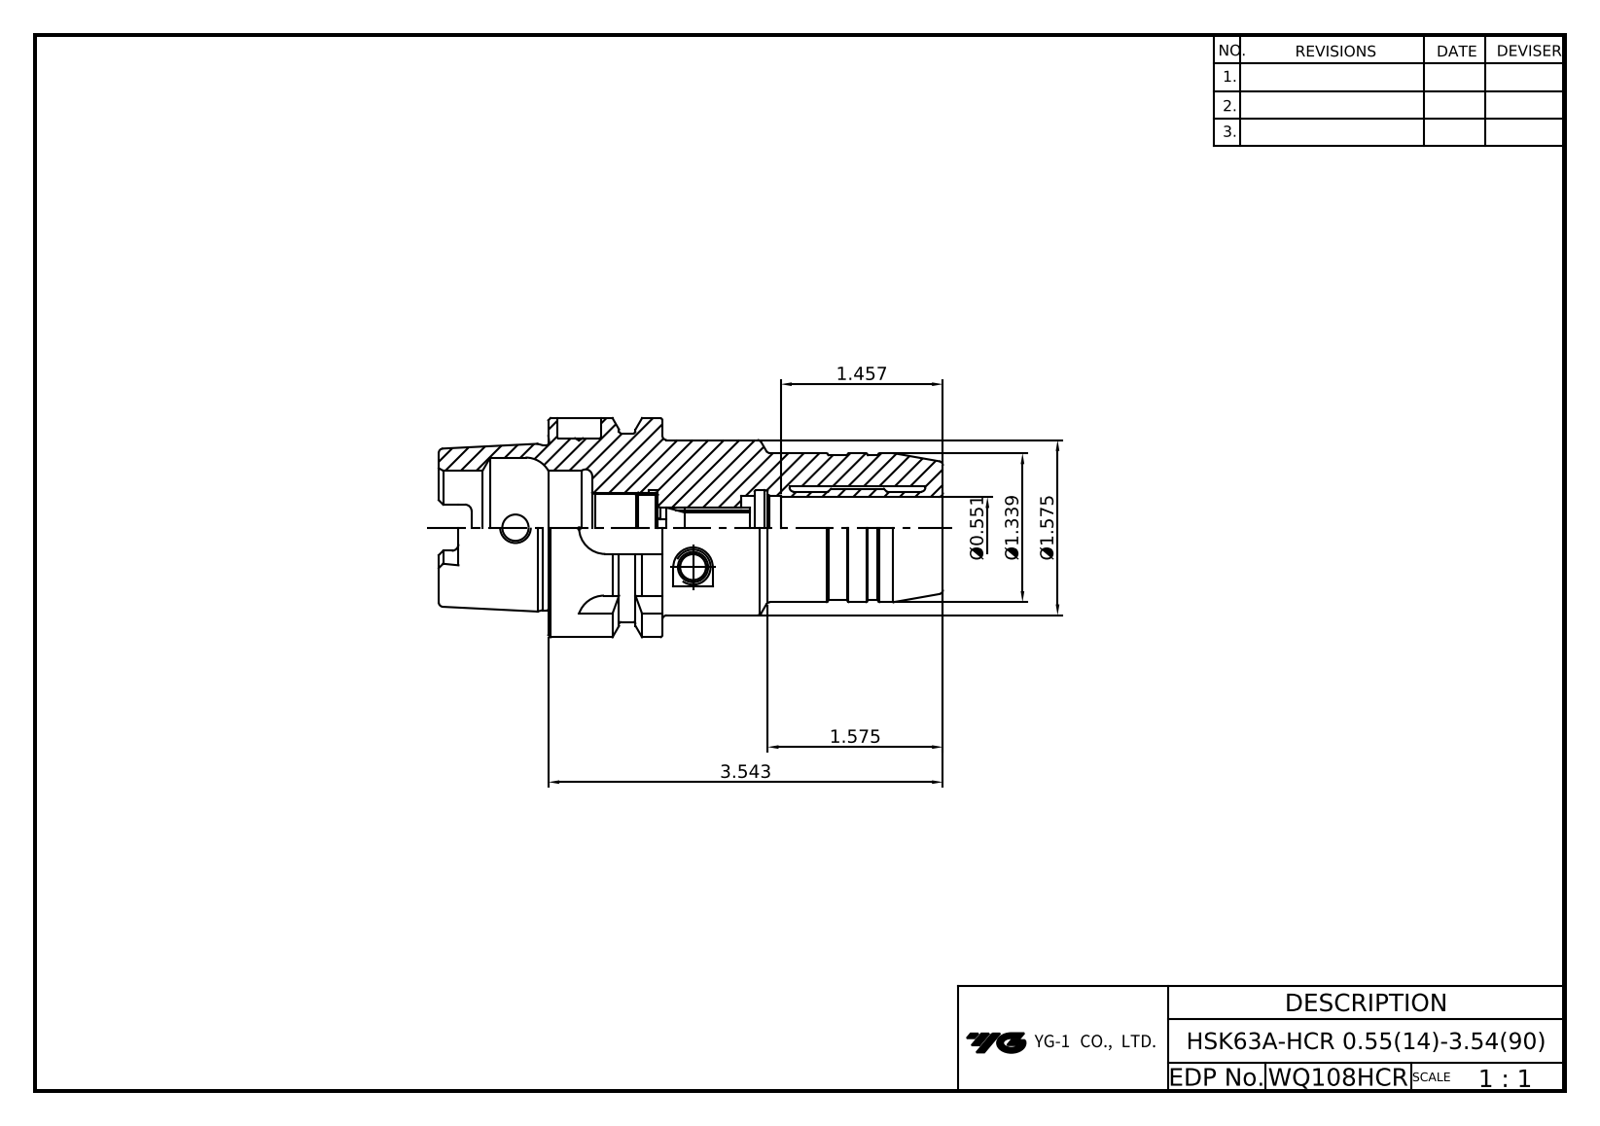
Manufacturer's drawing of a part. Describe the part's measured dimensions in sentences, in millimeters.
The part is named "WQ108HCR-HSK63A-HCR14-90". Its 3-D file was written by "PRO/ENGINEER BY PARAMETRIC TECHNOLOGY CORPORATION, 2012130 (CONFIG_CONTROL_DESIGN)". It is 1 solid with 217 faces: 58 planar, 63 cylindrical and 96 other. Overall it measures 122 by 63 by 63 millimeters. Its volume is 146 082 cubic millimeters and its surface area 32 274 square millimeters. Round holes: 1 of diameter 7.5, 1 of diameter 9, 1 of diameter 10, 1 of diameter 14, 1 of diameter 14.6, 1 of diameter 17, 1 of diameter 17.1, 1 of diameter 18, 1 of diameter 19, 1 of diameter 40. Round bosses or shafts: 1 of diameter 63, 1 of diameter 55, 1 of diameter 50, 1 of diameter 48.04, 1 of diameter 34, 1 of diameter 33. Partial cylindrical surfaces (rounded edges, fillets, slot ends): 6 of radius 1.5, 4 of radius 2.88, 4 of radius 8. The main face-to-face distances are 26, 10, 16, 32, 90, 80, 64, 42, 6.12, 9.88.
